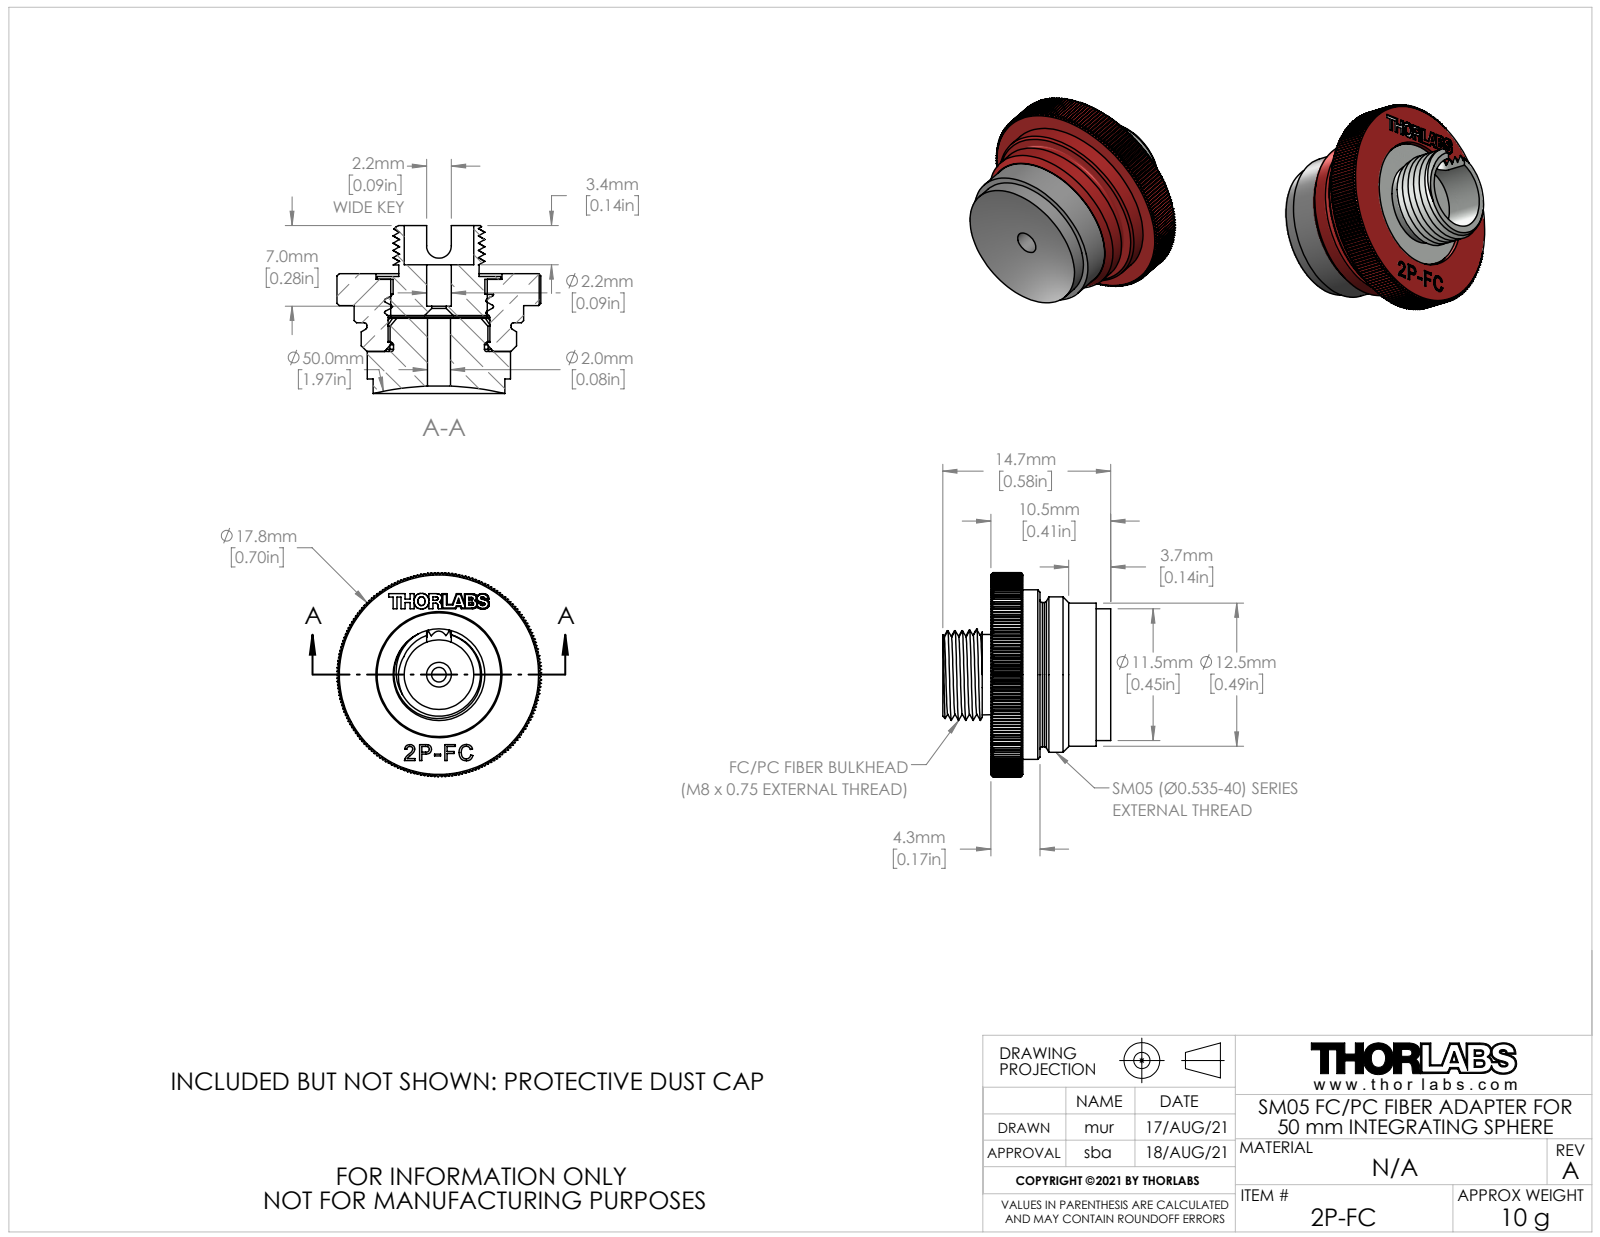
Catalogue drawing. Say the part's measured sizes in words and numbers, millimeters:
The part is named "21.08.19_2P-FC_FC-Adapter w. Sphere Radius_WEB". Its 3-D file was written by "SolidWorks 2019 (AUTOMOTIVE_DESIGN)". It is 3 solids with 1266 faces: 902 planar, 248 cylindrical and 116 other. Overall it measures 17.8 by 17.8 by 14.67 millimeters. Its volume is 1 655 cubic millimeters and its surface area 2 106 square millimeters. Round holes: 1 of diameter 1.27, 1 of diameter 2, 1 of diameter 2.16, 1 of diameter 6.07, 1 of diameter 8.43, 1 of diameter 11. Round bosses or shafts: 1 of diameter 14.8, 1 of diameter 13.56, 1 of diameter 12.6, 1 of diameter 12.5, 1 of diameter 11.5, 1 of diameter 10.79, 1 of diameter 8. Partial cylindrical surfaces (rounded edges, fillets, slot ends): 4 of radius 1.7, 4 of radius 1.79, 4 of radius 2, 2 of radius 1.05, 2 of radius 1.26, 2 of radius 1.35, 1 of radius 1.08, 1 of radius 4.76. The main face-to-face distances are 3.4, 0.5, 3.15, 3.65, 3.8, 2.8, 2.3, 1.1, 3.9, 4.
